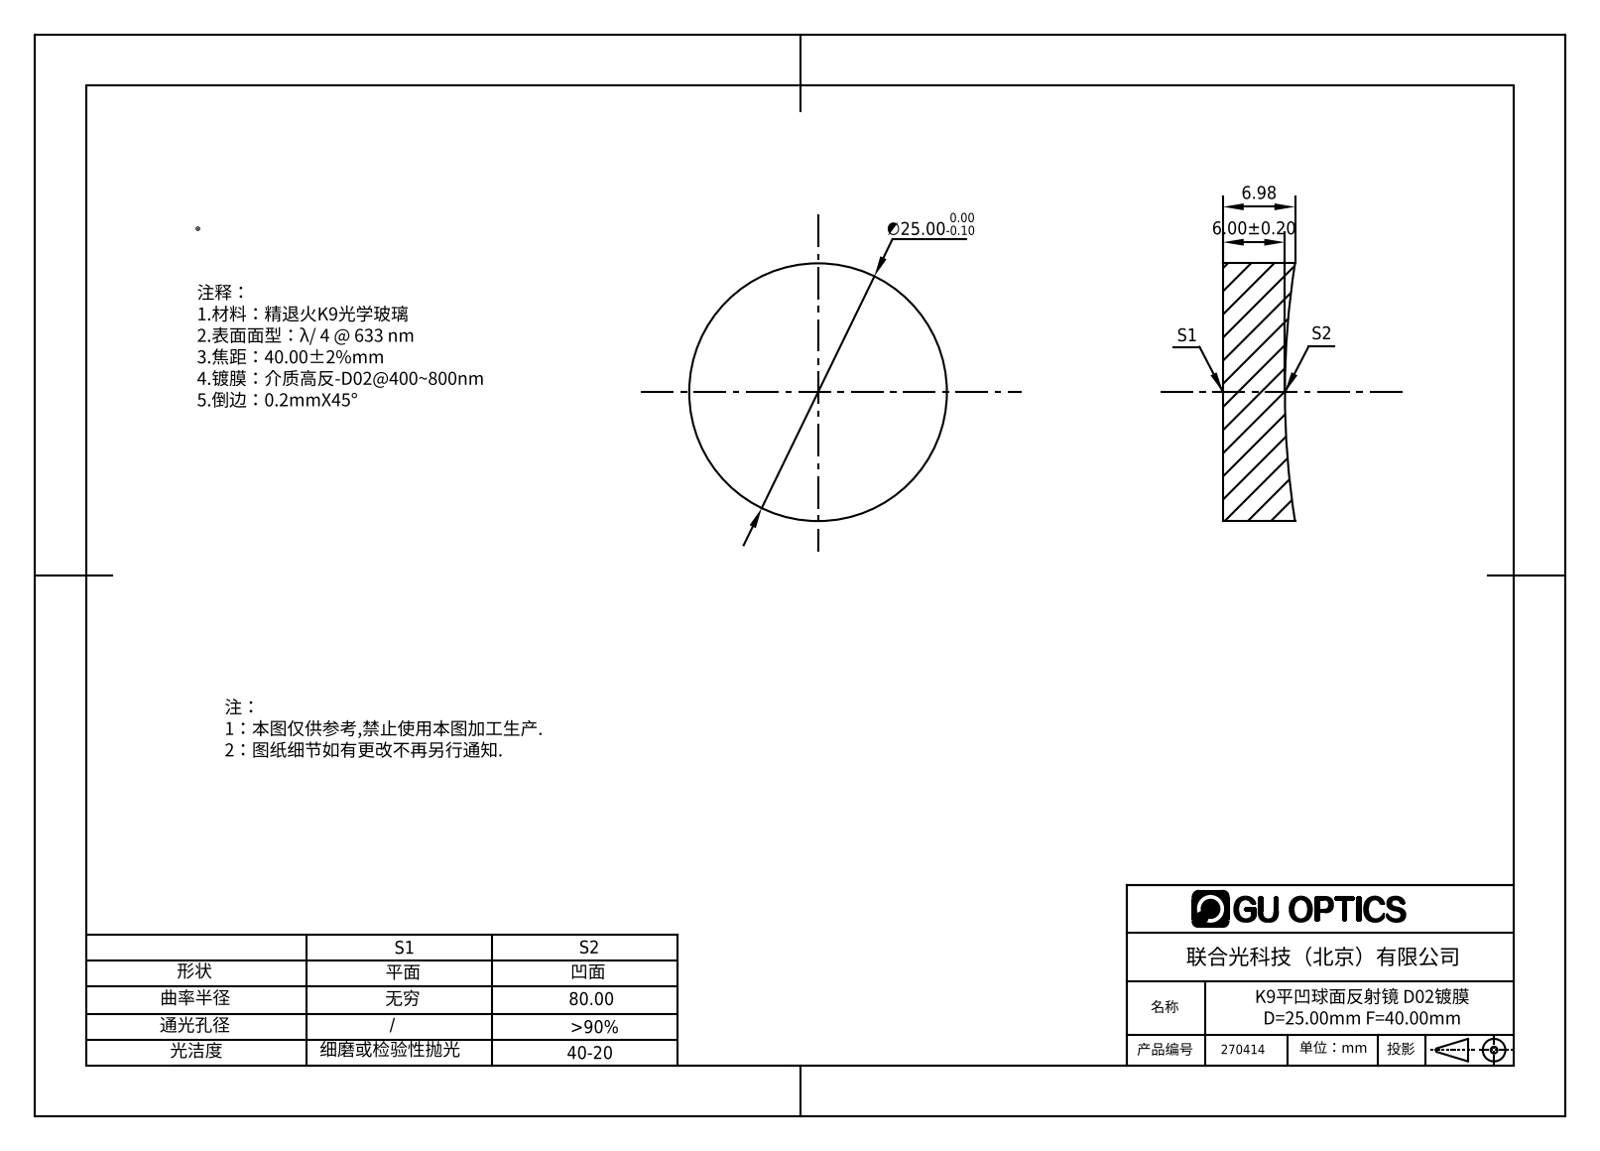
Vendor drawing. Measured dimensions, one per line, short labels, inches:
name: 270024
written by: SolidWorks 2016 (AUTOMOTIVE_DESIGN)
unit: in
bodies: 1 solid, 5 faces (1 planar, 2 cylindrical, 2 other)
size: 0.984 × 0.984 × 0.275
volume: 0.194 in³; area: 2.376 in²
bosses: 1× ⌀0.984
